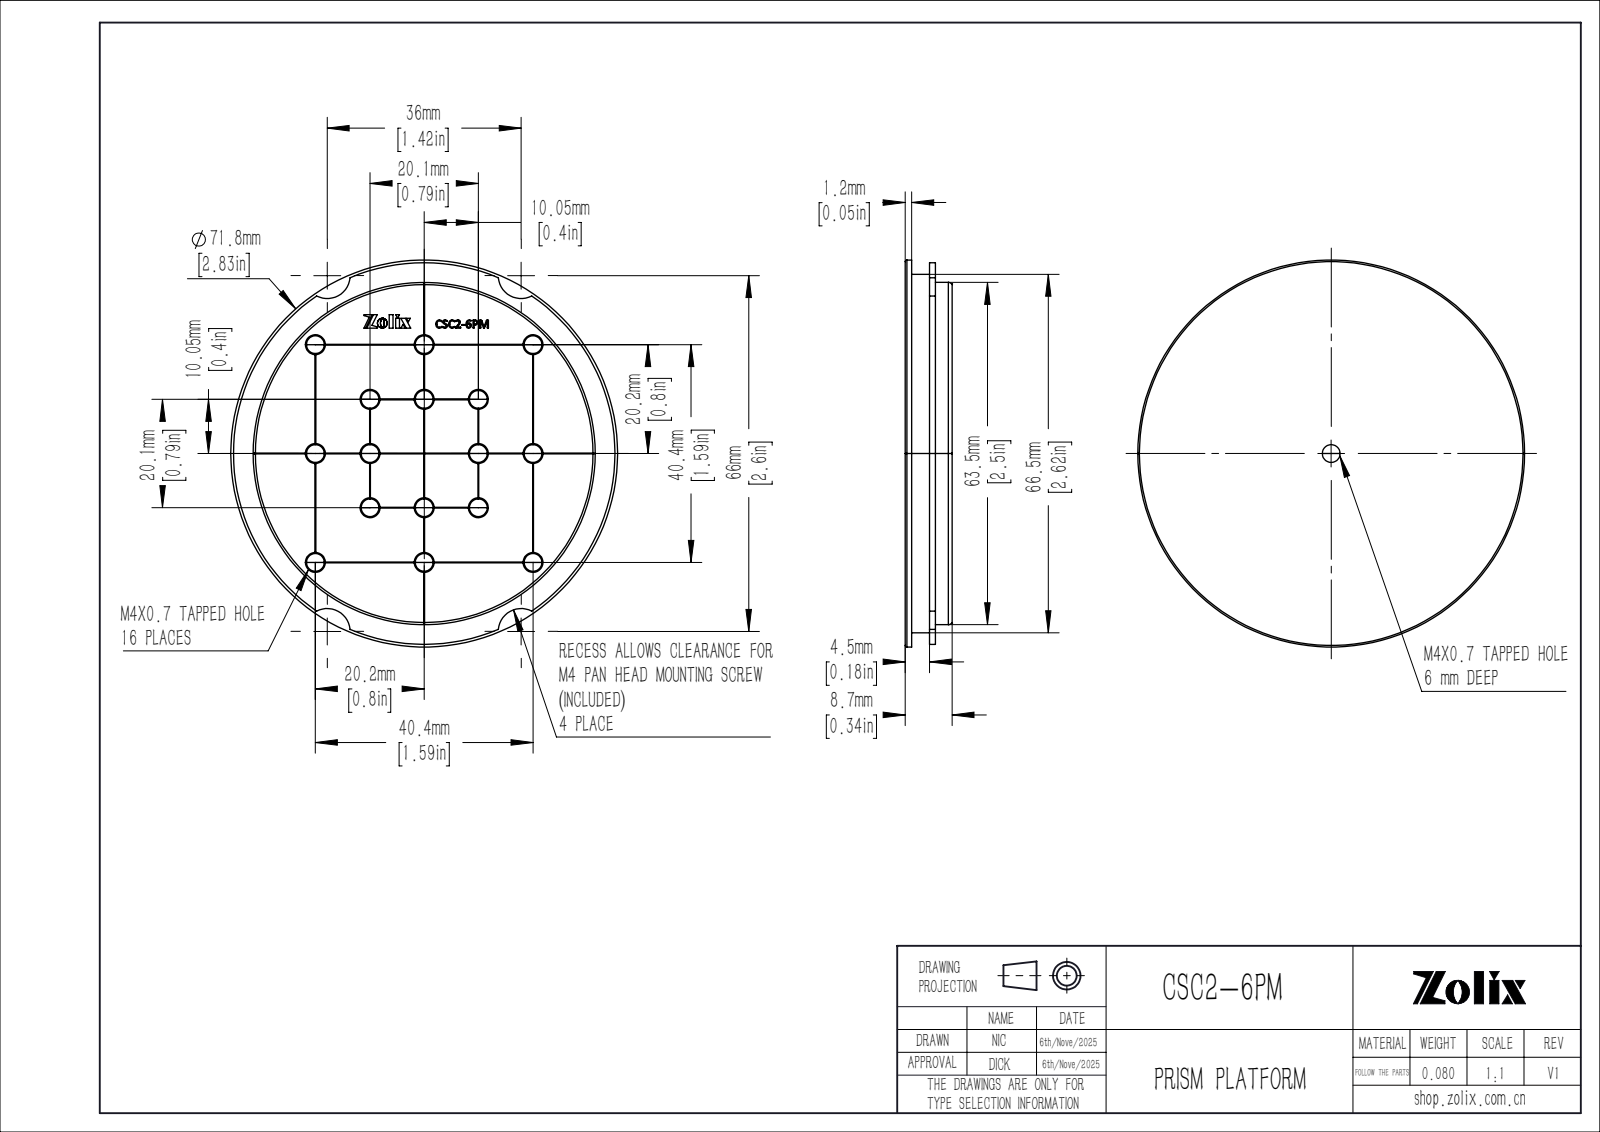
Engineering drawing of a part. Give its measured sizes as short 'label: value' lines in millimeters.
name: CSC2-6PM
written by: SolidWorks 2020 (CONFIG_CONTROL_DESIGN)
unit: mm
bodies: 1 solid, 502 faces (306 planar, 49 cylindrical, 147 other)
size: 71.8 × 71.8 × 8.7
volume: 29 481 mm³; area: 11 811 mm²
holes: 17× ⌀3.3
bosses: 1× ⌀71.8, 1× ⌀70.8, 1× ⌀66.5, 1× ⌀63.5
rounds: 4× R4.25
face distances: 8.7, 3.1, 5.6, 1.2, 7.5, 4.4, 4.5, 4.2, 1.1, 3.3
hole spacings: 10.05, 20.2, 14.21, 14.28, 22.47, 22.56, 22.61, 28.57
